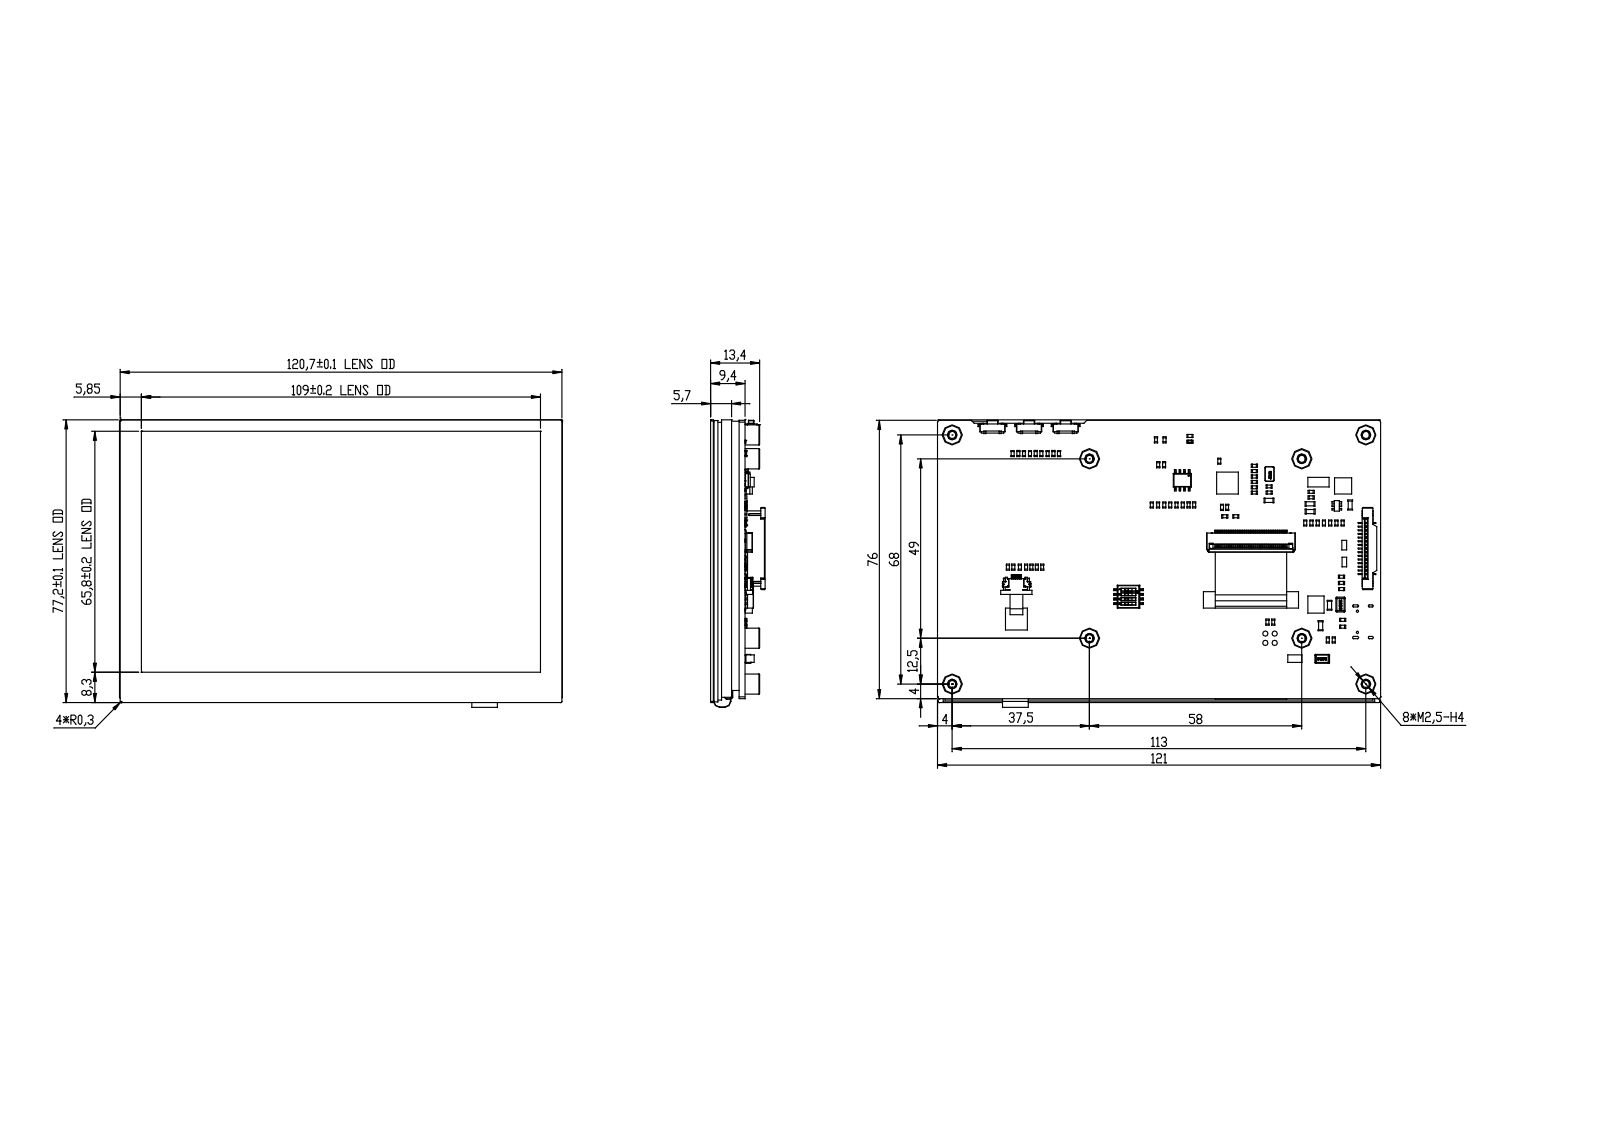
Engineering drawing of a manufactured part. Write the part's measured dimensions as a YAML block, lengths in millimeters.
part_name: "5INCH-HDMI-LCD-H-TP; 5INCH-LCD-H-800X480; 5DP-CAPLCD-EVA; STUDS-M2_5XH4 (+8 more)"
step_written_by: "CREO PARAMETRIC BY PTC INC, 2021063 (CONFIG_CONTROL_DESIGN)"
units: millimeters
bodies: {solids: 245, faces: 6785, planar: 5618, cylindrical: 790, other: 377}
overall_size: [121, 78.61, 14.88]
volume: 62875
surface_area: 70902
round_holes:
  - {diameter: 2.5, count: 8}
  - {diameter: 4.3, count: 8}
  - {diameter: 0.8, count: 6}
  - {diameter: 1.45, count: 4}
  - {diameter: 0.65, count: 2}
  - {diameter: 0.43, count: 1}
round_bosses_or_shafts:
  - {diameter: 5.5, count: 8}
  - {diameter: 4.19, count: 8}
partial_cylinders:
  - {radius: 0.1, count: 115}
  - {radius: 0.2, count: 19}
  - {radius: 0.3, count: 17}
  - {radius: 0.23, count: 10}
  - {radius: 0.25, count: 8}
  - {radius: 1.5, count: 6}
  - {radius: 1.6, count: 6}
  - {radius: 0.5, count: 5}
face_to_face_distances: [3.7, 2.1, 1.6, 7.4, 5.8, 4.7, 1.95, 5.65, 9.35, 7.75]
hole_center_spacings: [2.54, 10, 2.3, 3.59, 7.52, 7.7, 10.03, 12.3]
